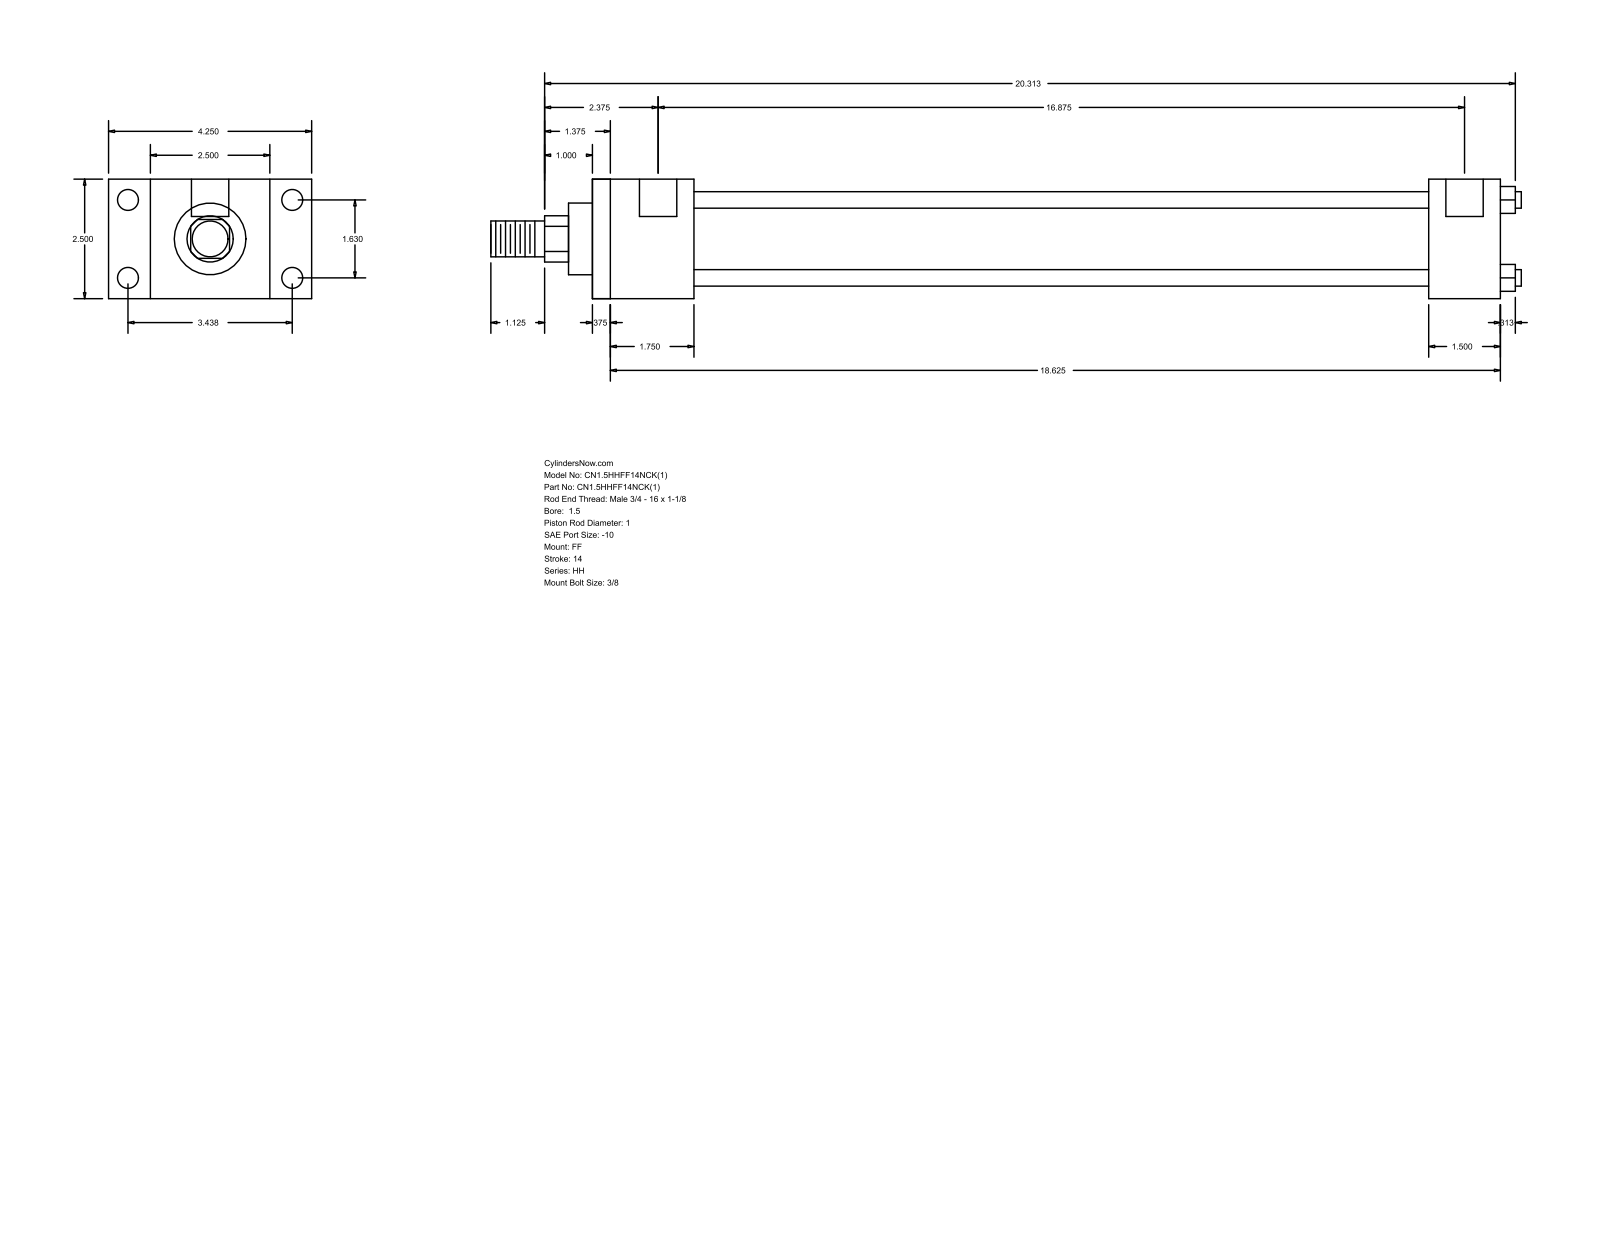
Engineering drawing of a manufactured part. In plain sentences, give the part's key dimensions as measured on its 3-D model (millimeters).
The part is named "HH_FF__0150_1". Its 3-D file was written by "GSSL Pune (CONFIG_CONTROL_DESIGN)". It is 0 solids with 92 faces: 64 planar, 28 cylindrical and 0 other. Overall it measures 547.69 by 107.95 by 63.5 millimeters. Round holes: 4 of diameter 5.56, 4 of diameter 11.13, 2 of diameter 19.84. Round bosses or shafts: 4 of diameter 8.76, 1 of diameter 44.45, 1 of diameter 38.1, 1 of diameter 25.4, 1 of diameter 19.05. Partial cylindrical surfaces (rounded edges, fillets, slot ends): 1 of radius 12.29. The main face-to-face distances are 63.5, 482.6, 9.52, 473.08, 38.1, 53.98, 44.46, 428.62, 444.5, 434.98. The hole center spacings are 1.59, 41.4, 87.32, 96.64, 430.21, 431.8, 428.62.
